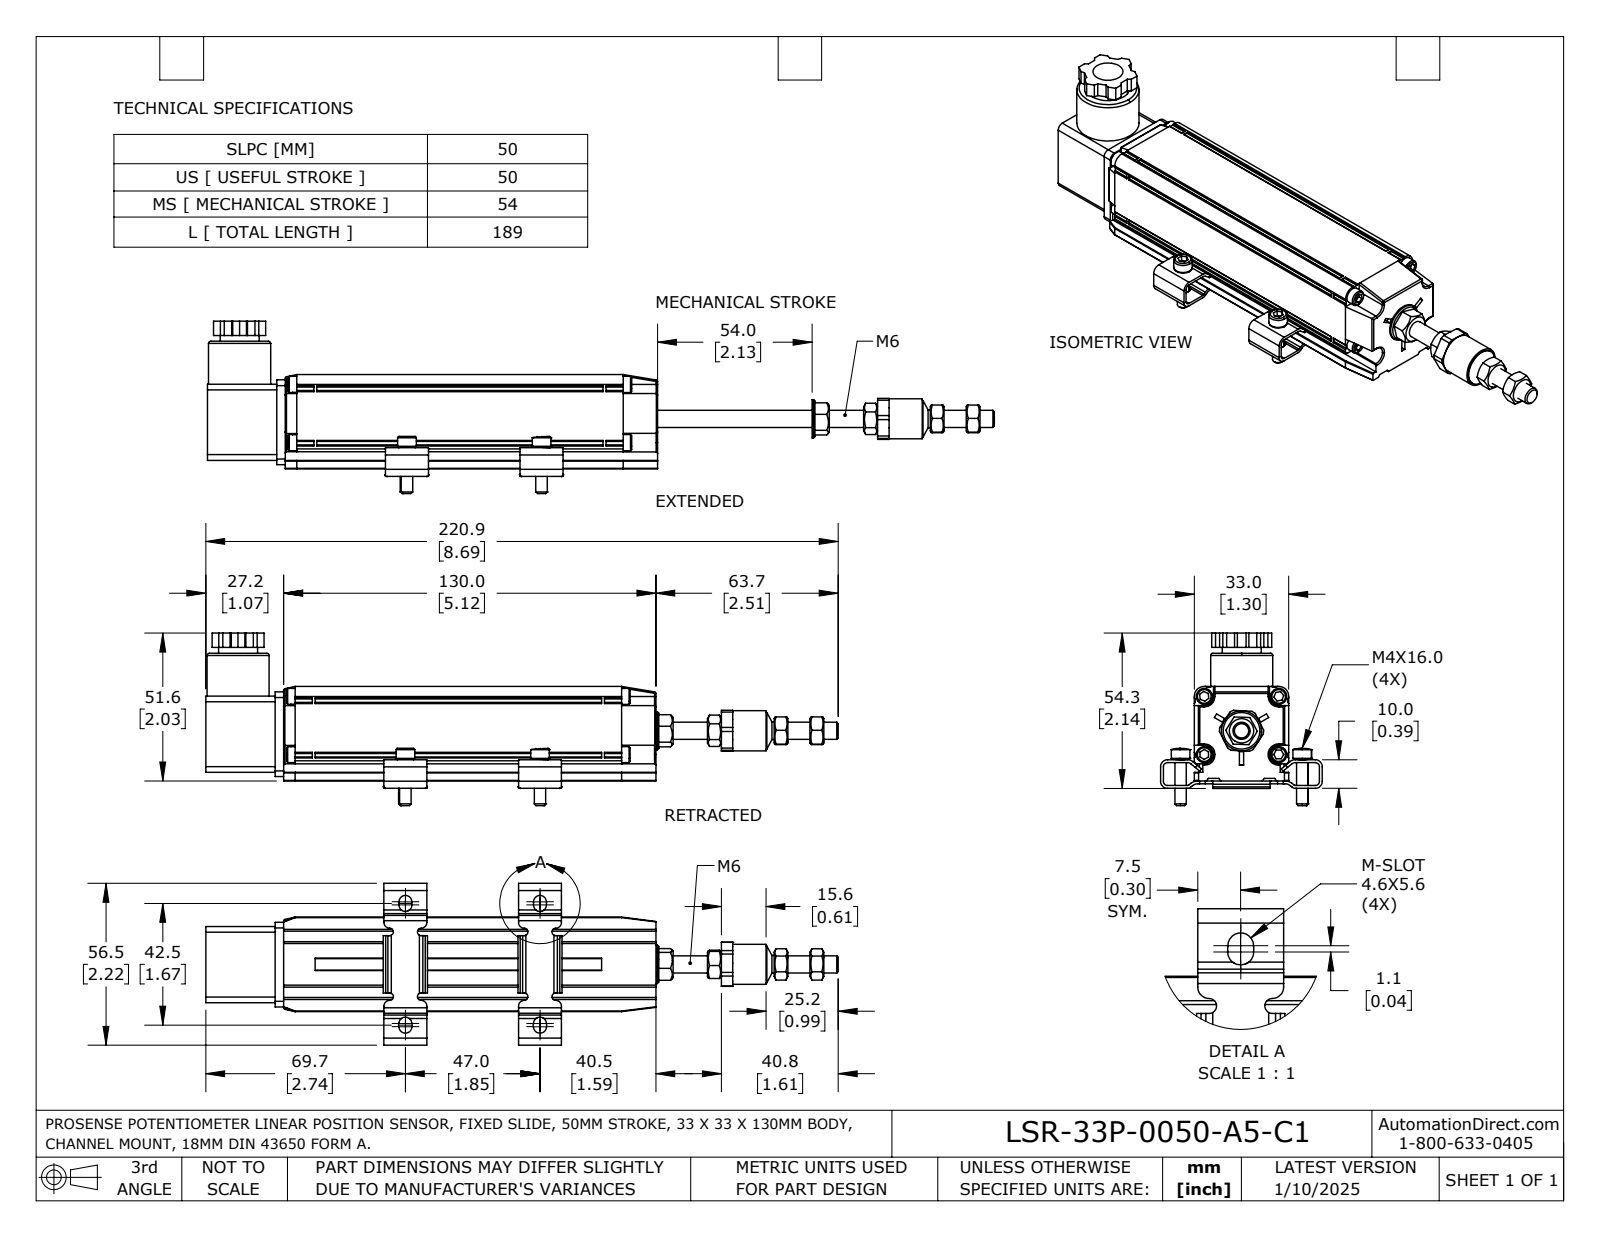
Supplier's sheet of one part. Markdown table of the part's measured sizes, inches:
| quantity | value |
| --- | --- |
| part name | LSR-33P-0050-A5-C1 |
| STEP written by | SolidWorks 2023 (AUTOMOTIVE_DESIGN) |
| units | inches |
| bodies | 15 solids, 977 faces (645 planar, 259 cylindrical, 73 other) |
| overall size | 8.695 × 2.37 × 2.224 |
| volume | 9.211 in³ |
| surface area | 88.87 in² |
| round holes (diameter × count) | 0.106 × 4, 0.13 × 4, 0.11 × 1, 0.169 × 1, 0.205 × 1, 0.209 × 1, 0.232 × 1, 0.276 × 1, 0.285 × 1, 0.394 × 1, 0.413 × 1, 0.573 × 1 |
| round bosses / shafts (diameter × count) | 0.157 × 5, 0.118 × 5, 0.256 × 4, 0.22 × 4, 0.854 × 1, 0.551 × 1, 0.535 × 1, 0.528 × 1 |
| partial cylindrical surfaces (radius × count) | 0.079 × 28, 0.02 × 27, 0.008 × 16, 0.051 × 8, 0.059 × 8, 0.089 × 8, 0.118 × 8, 0.039 × 4 |
| main face-to-face distances | 1.299, 0.039, 0.118, 0.063, 0.22, 0.102, 1.181, 0.984, 0.071, 0.079 |
| hole center spacings | 0.047, 0.583, 0.607, 0.696, 0.73, 0.799, 1.024, 1.299 |
